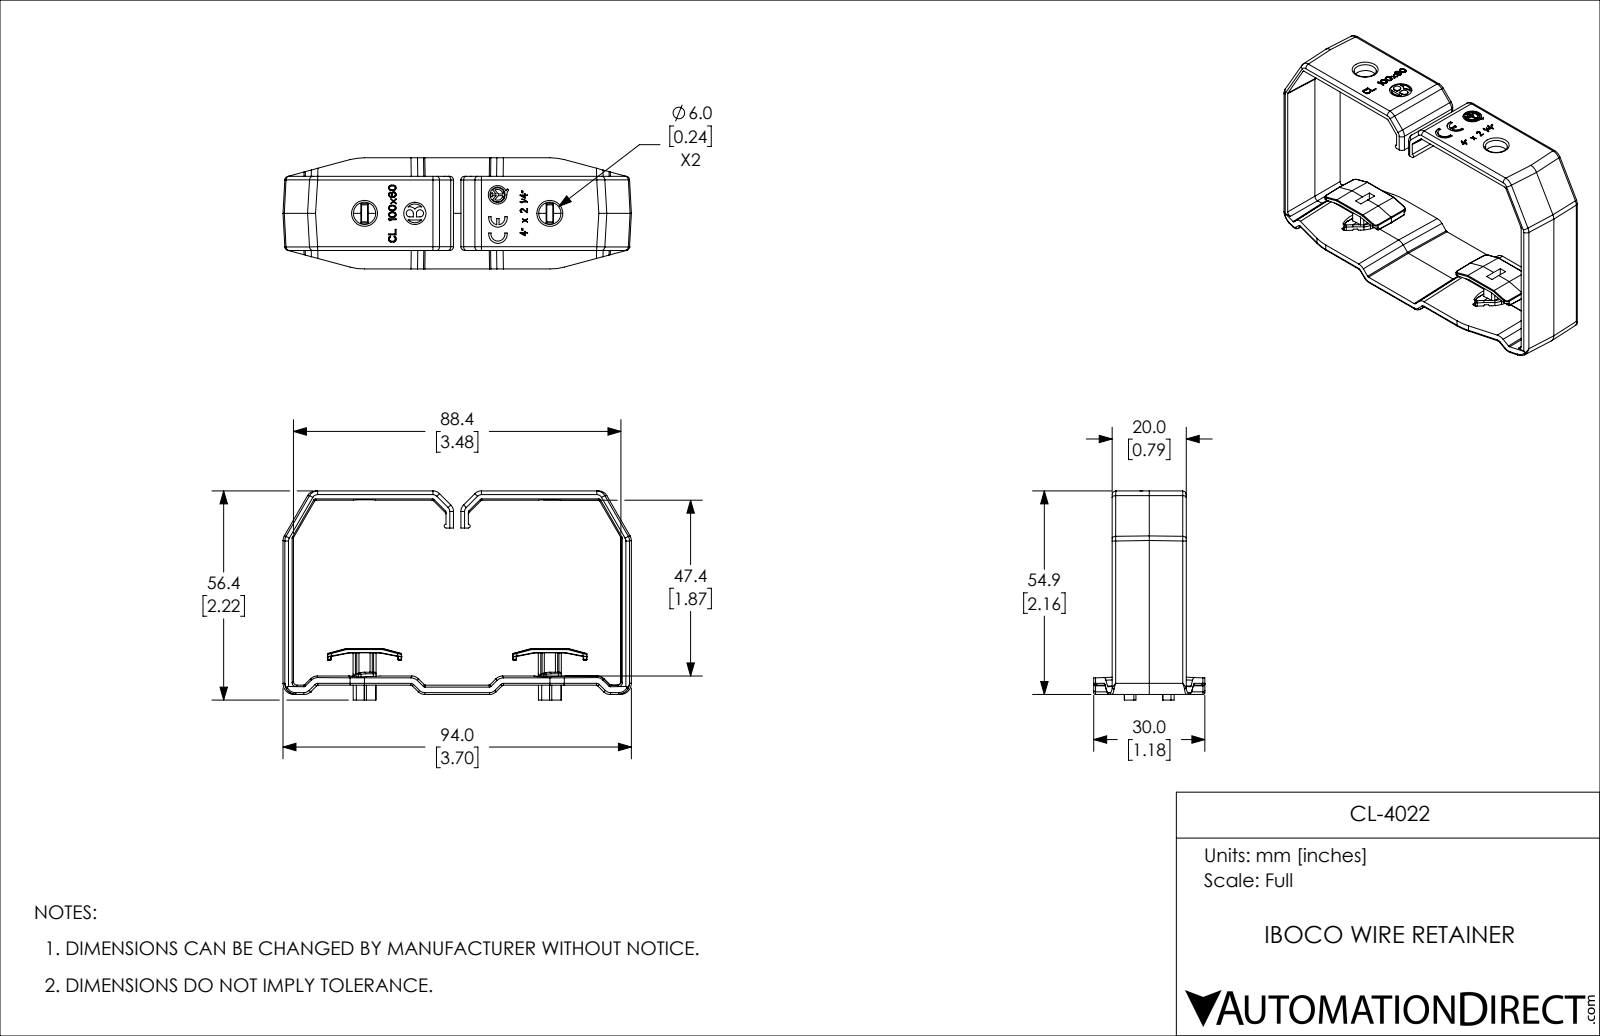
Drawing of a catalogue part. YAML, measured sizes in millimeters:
part_name: "CL-4022"
step_written_by: "SolidWorks 2019 (CONFIG_CONTROL_DESIGN)"
units: millimeters
bodies: {solids: 1, faces: 1014, planar: 658, cylindrical: 279, other: 77}
overall_size: [94, 56.4, 30]
volume: 15200
surface_area: 15930
round_holes:
  - {diameter: 6, count: 3}
  - {diameter: 5, count: 1}
round_bosses_or_shafts:
  - {diameter: 4.1, count: 1}
partial_cylinders:
  - {radius: 0.5, count: 66}
  - {radius: 0.2, count: 36}
  - {radius: 1, count: 34}
  - {radius: 2.5, count: 30}
  - {radius: 0.3, count: 12}
  - {radius: 0.4, count: 12}
  - {radius: 0.7, count: 4}
  - {radius: 1.2, count: 4}
face_to_face_distances: [2.5, 47.3, 52.4, 88.3, 93.9, 54.9, 49.9, 35.4, 20, 2]
hole_center_spacings: [13.6, 15, 22.9, 36.2, 36.4, 50]
